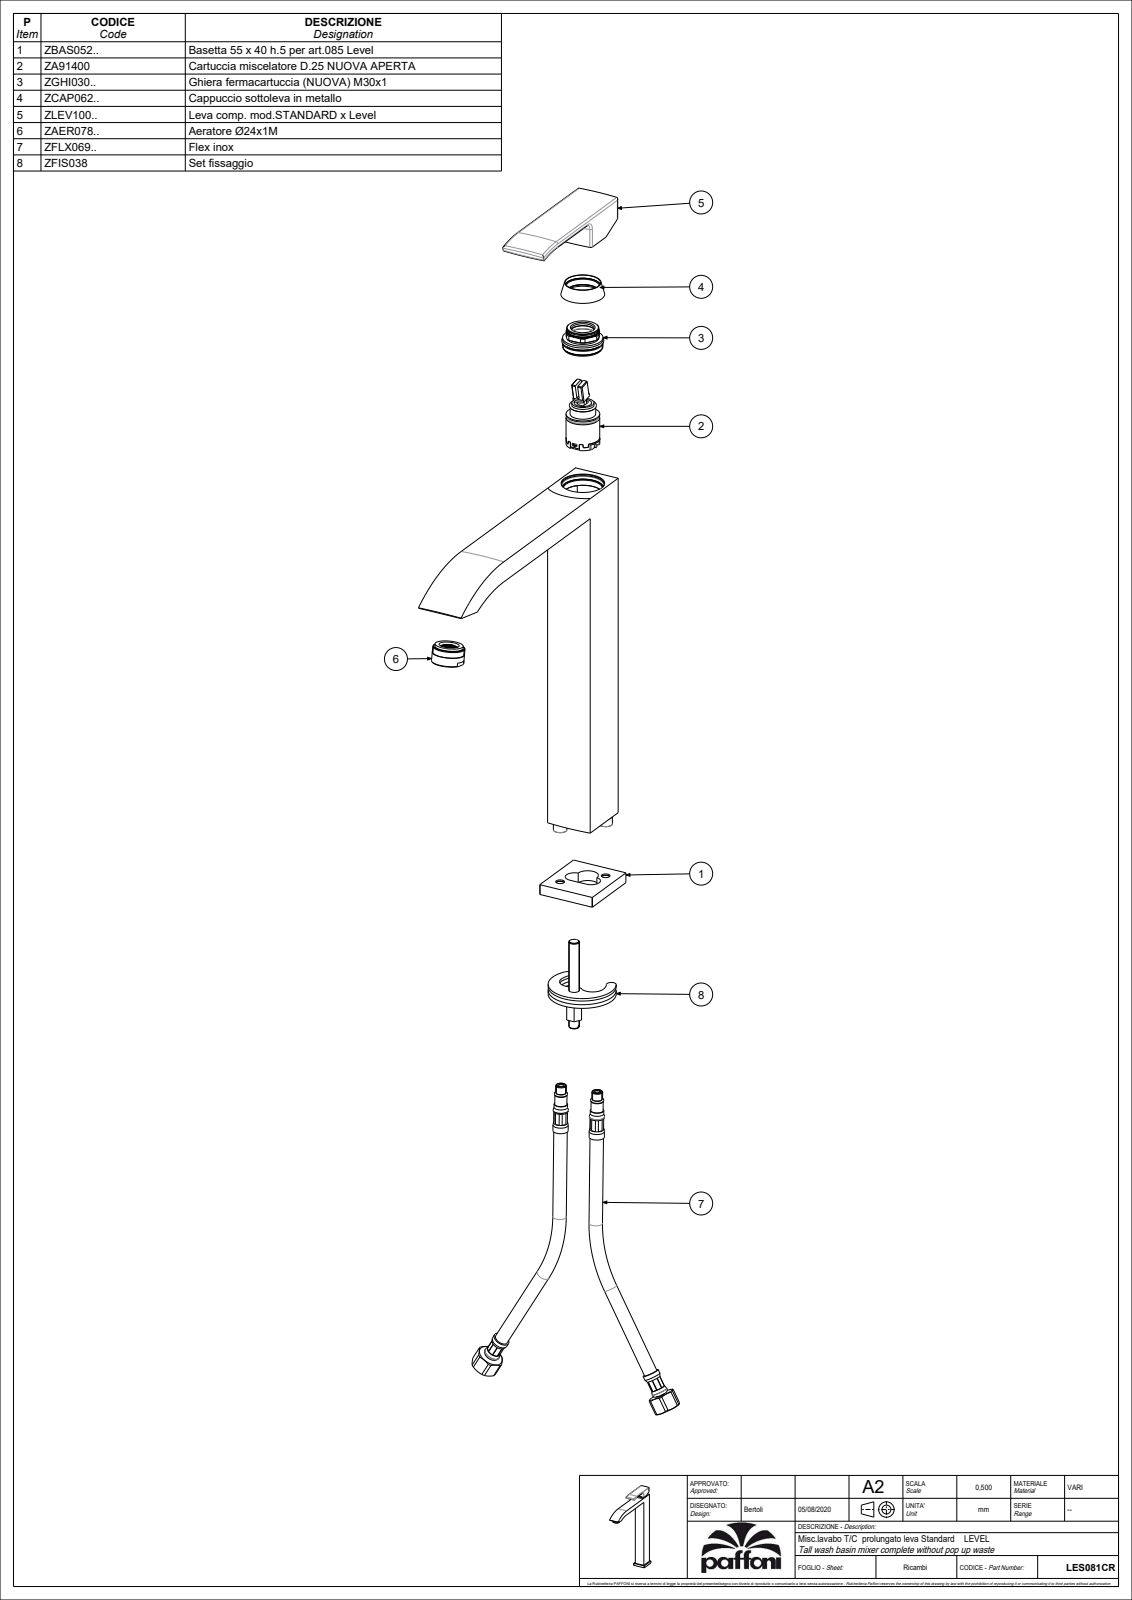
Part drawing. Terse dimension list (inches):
name: LES081CR
written by: CREO PARAMETRIC BY PTC INC, 2020044 (CONFIG_CONTROL_DESIGN)
unit: in
bodies: 0 solids, 83 faces (32 planar, 29 cylindrical, 22 other)
size: 12.246 × 9.341 × 1.772
bosses: 1× ⌀0.945
rounds: 8× R0.059, 8× R0.079, 2× R0.031, 2× R11.811, 1× R0.252, 1× R1.319, 1× R1.366, 1× R4.252
face distances: 1.398, 11.094, 0.315, 10.78, 1.388, 0.187, 1.378, 0.197, 1.575, 1.585
